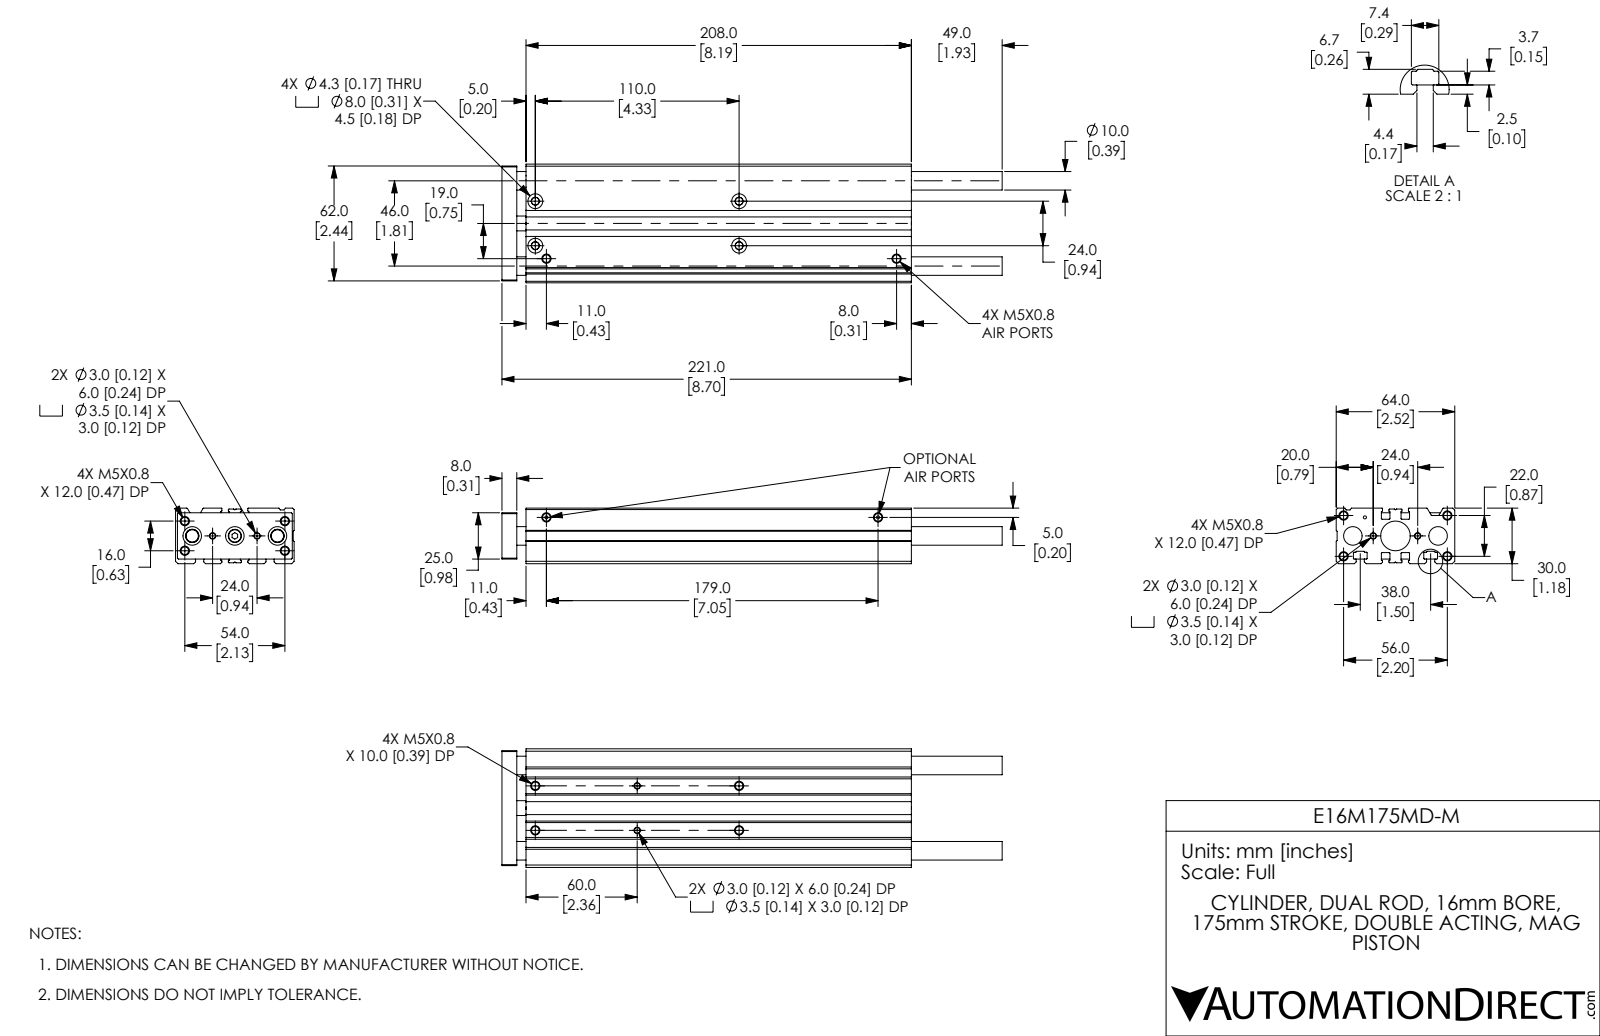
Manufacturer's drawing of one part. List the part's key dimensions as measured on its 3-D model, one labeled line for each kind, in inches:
Part name (STEP PRODUCT): E16M175MD-M_BODY; E16M175MD-M_ENDPLATE; E16M175MD-M
STEP written by: SolidWorks 2019 (CONFIG_CONTROL_DESIGN)
Units: inches
Bodies: 5 solids, 411 faces (133 planar, 192 cylindrical, 86 other)
Overall size (bounding box): 10.63 × 2.52 × 1.181
Volume: 20.87 in³ · Surface area: 179.9 in²
Round holes (diameter × count): ⌀0.163 ×16, ⌀0.118 ×4, ⌀0.138 ×4, ⌀0.169 ×4, ⌀0.315 ×4, ⌀0.066 ×3, ⌀0.197 ×3, ⌀0.394 ×3, ⌀0.28 ×2, ⌀0.394 ×1, ⌀0.63 ×1, ⌀0.63 ×1
Round bosses / shafts (diameter × count): ⌀0.315 ×1, ⌀0.28 ×1
Partial cylindrical surfaces — rounded edges, fillets, slot ends (radius × count): R0.008 ×22, R0.016 ×20, R0.01 ×8, R0.012 ×6, R0.02 ×4
Main face-to-face distances: 1.181, 0.02, 0.236, 2.52, 1.142, 0.961, 0.945, 1.378, 0.138, 1.559
Hole centre spacings: 0.124, 0.352, 0.476, 0.669, 0.749, 0.765, 0.945, 1.109
